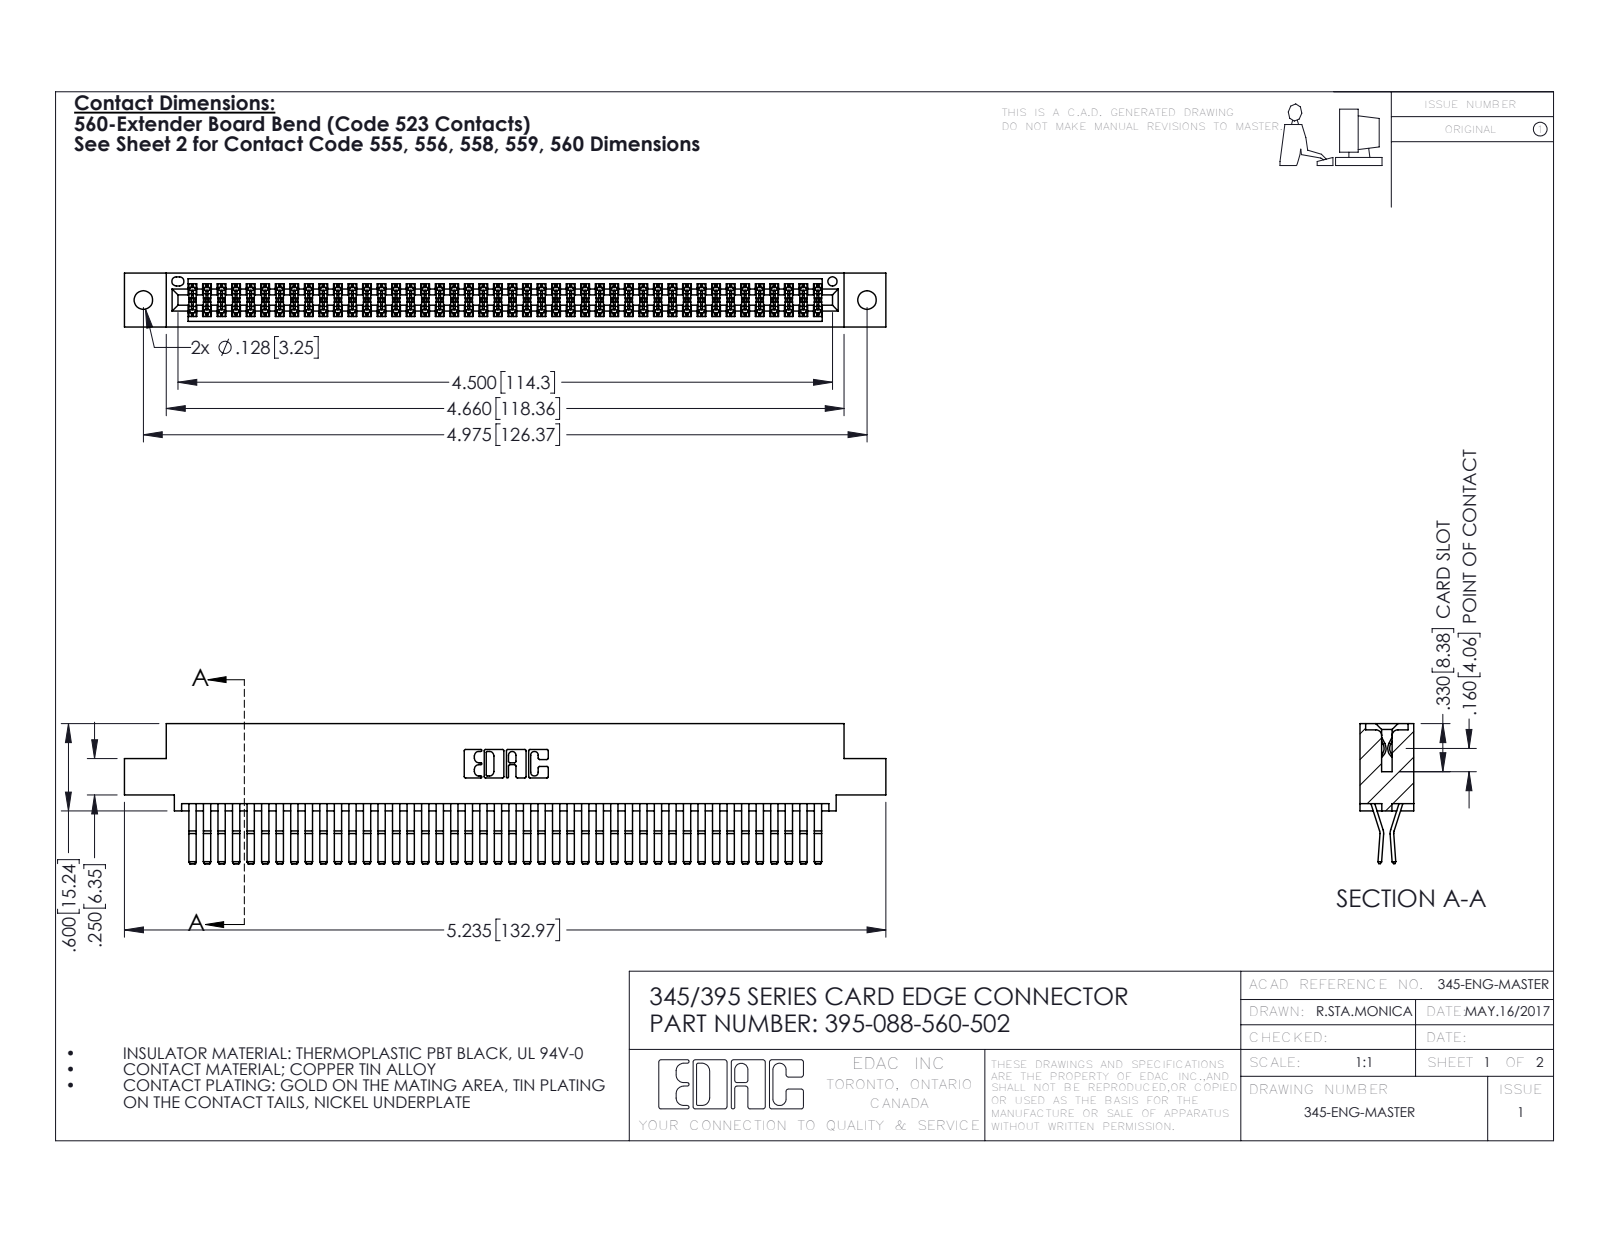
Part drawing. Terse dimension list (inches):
name: 395-088-560-502; 345-292-001_560 Tail; 345 Part_0.110 Offset - 0.128 Dia
written by: SolidWorks 2016 (CONFIG_CONTROL_DESIGN)
unit: in
bodies: 89 solids, 4706 faces (2988 planar, 1718 cylindrical, 0 other)
size: 5.235 × 0.962 × 0.37
volume: 0.818 in³; area: 32.79 in²
holes: 2× ⌀0.128, 1× ⌀0.064
rounds: 132× R0.006, 22× R0.01, 6× R0.007, 6× R0.031, 3× R0.026, 2× R0.01, 2× R0.014, 2× R0.019
face distances: 0.025, 0.298, 0.072, 0.37, 0.2, 0.098, 0.272, 0.225, 0.175, 0.149
hole spacings: 0.27, 4.739, 4.975
